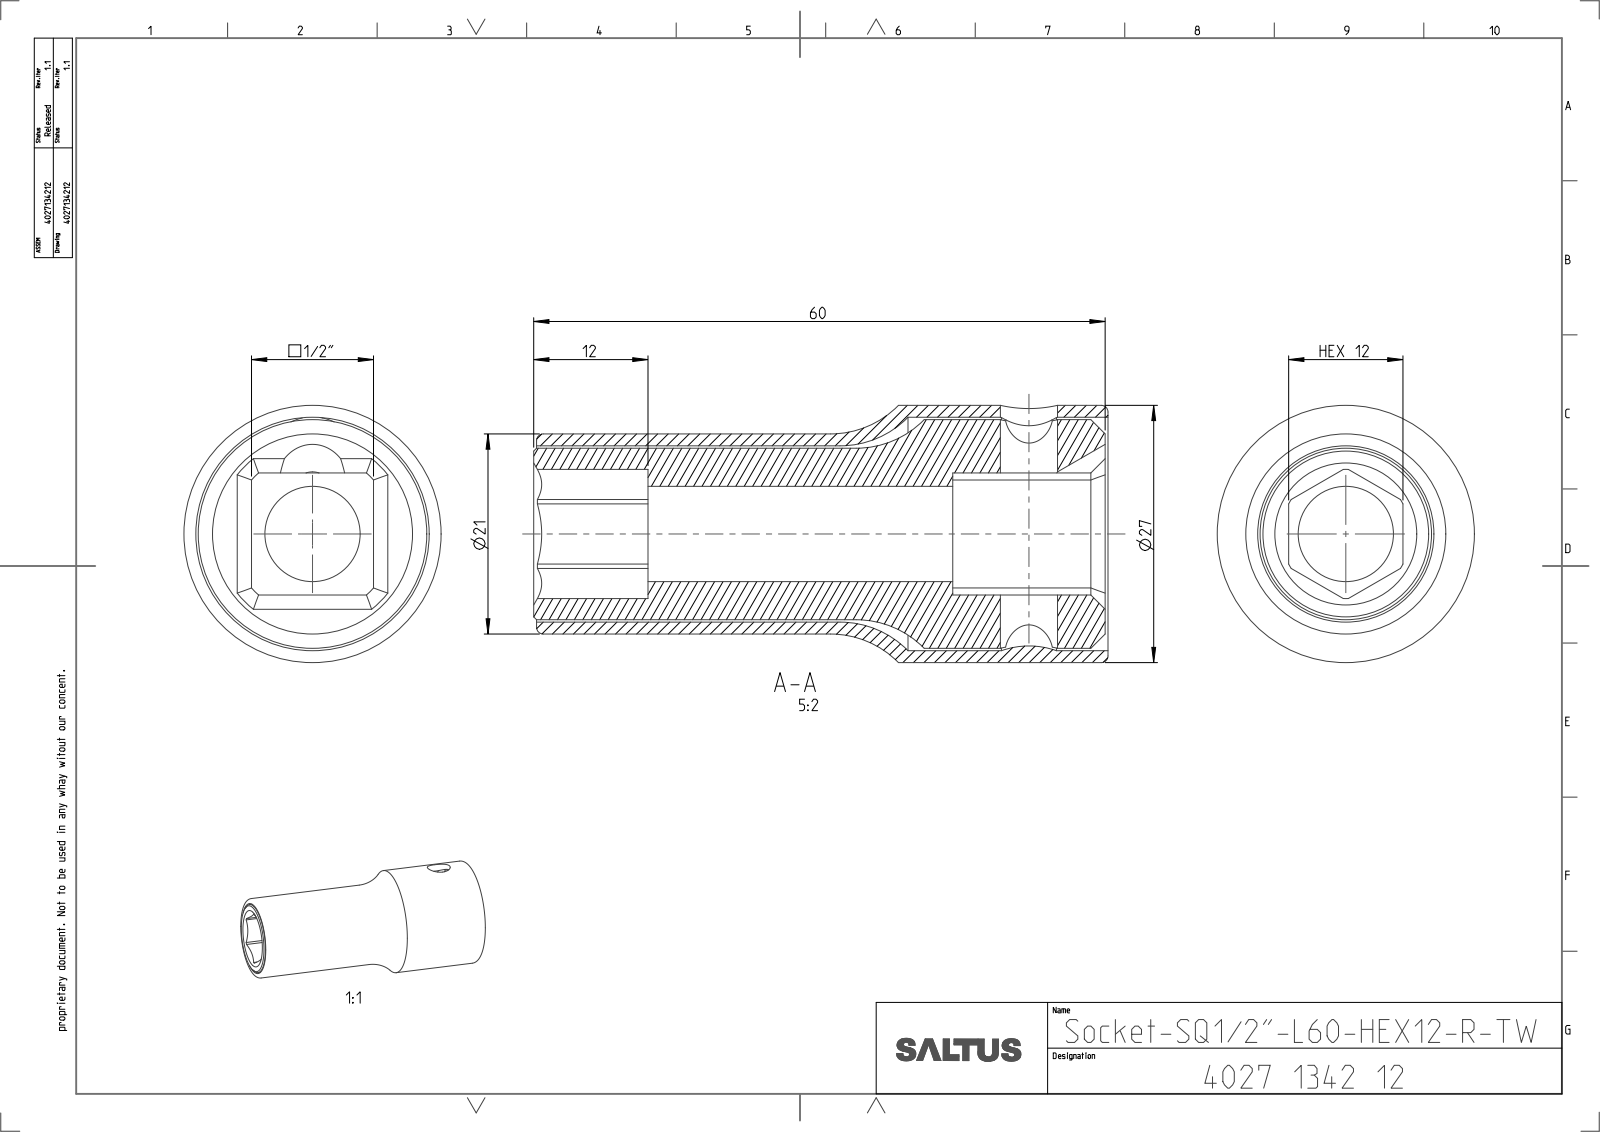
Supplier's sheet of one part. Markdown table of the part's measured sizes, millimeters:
| quantity | value |
| --- | --- |
| part name | 4027130212; 4027299254; 4027134212_ASM |
| STEP written by | CREO PARAMETRIC BY PTC INC, 2022414 (CONFIG_CONTROL_DESIGN) |
| units | millimeters |
| bodies | 2 solids, 79 faces (21 planar, 35 cylindrical, 23 other) |
| overall size | 60.3 × 27 × 27 |
| volume | 17 405 mm³ |
| surface area | 15 238 mm² |
| round holes (diameter × count) | 6 × 1, 10 × 1, 18.5 × 1, 24.5 × 1 |
| round bosses / shafts (diameter × count) | 27 × 1, 24 × 1, 21 × 1, 18 × 1 |
| partial cylindrical surfaces (radius × count) | 4 × 1, 6.78 × 1, 8.55 × 1 |
| main face-to-face distances | 12.82, 12, 0.41, 12.41, 60, 16, 44, 48, 32, 16.3 |
